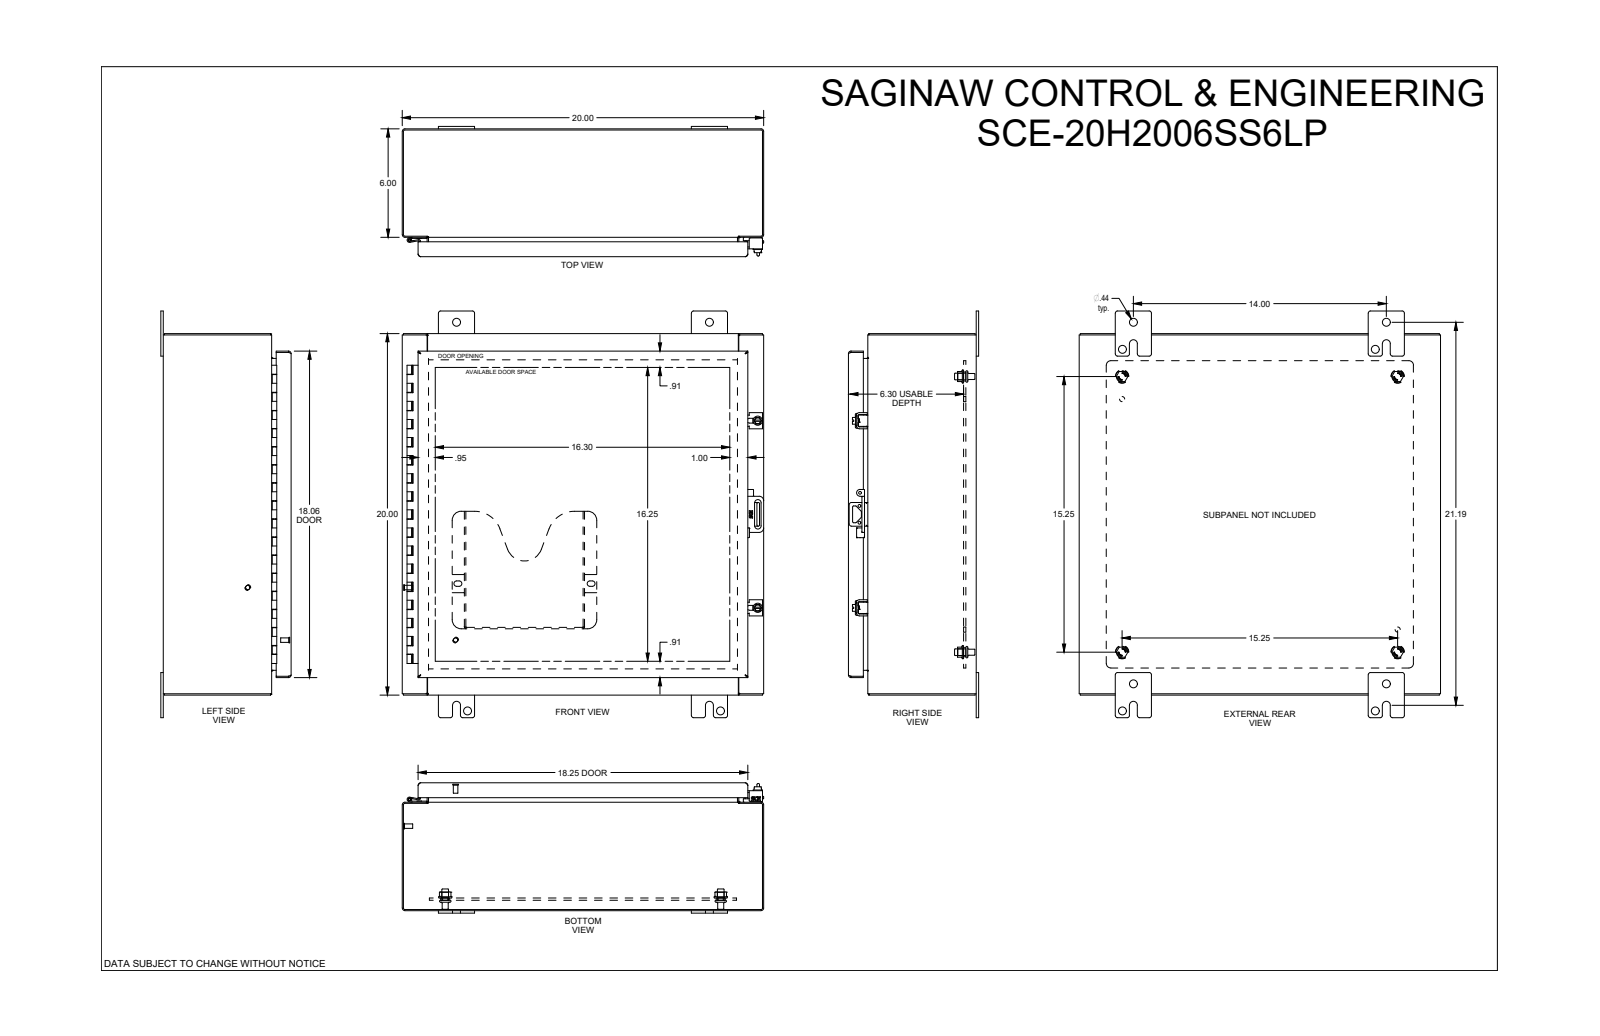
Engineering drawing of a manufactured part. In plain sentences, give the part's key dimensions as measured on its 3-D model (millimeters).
The part is named "SCE-20H2006SS6LP". Its 3-D file was written by "SolidWorks 2019 (CONFIG_CONTROL_DESIGN)". It is 0 solids with 3015 faces: 1210 planar, 622 cylindrical and 1183 other. Overall it measures 571.5 by 508 by 183.1 millimeters. Round holes: 8 of diameter 11.1, 5 of diameter 6.4, 4 of diameter 9.3, 4 of diameter 12.7, 3 of diameter 4.8, 3 of diameter 4.9, 2 of diameter 4.1, 2 of diameter 5.2, 2 of diameter 7.1, 1 of diameter 3.3, 1 of diameter 3.4. Round bosses or shafts: 7 of diameter 6.3, 5 of diameter 14.3, 4 of diameter 9.3, 4 of diameter 8.4, 3 of diameter 6.5, 3 of diameter 6.4, 3 of diameter 4.8, 2 of diameter 12.9. Partial cylindrical surfaces (rounded edges, fillets, slot ends): 108 of radius 0.3, 36 of radius 0.4, 30 of radius 0.7, 27 of radius 0.8, 27 of radius 3.2, 25 of radius 1.5, 22 of radius 1, 14 of radius 1.8. The main face-to-face distances are 1.9, 506.1, 177.7, 175.8, 1.9, 179.7, 177.7, 12.7, 15.9, 3.2. The hole center spacings are 355.6, 387.4, 77.9, 13.1, 31.8, 36.6, 41.1, 41.1.
